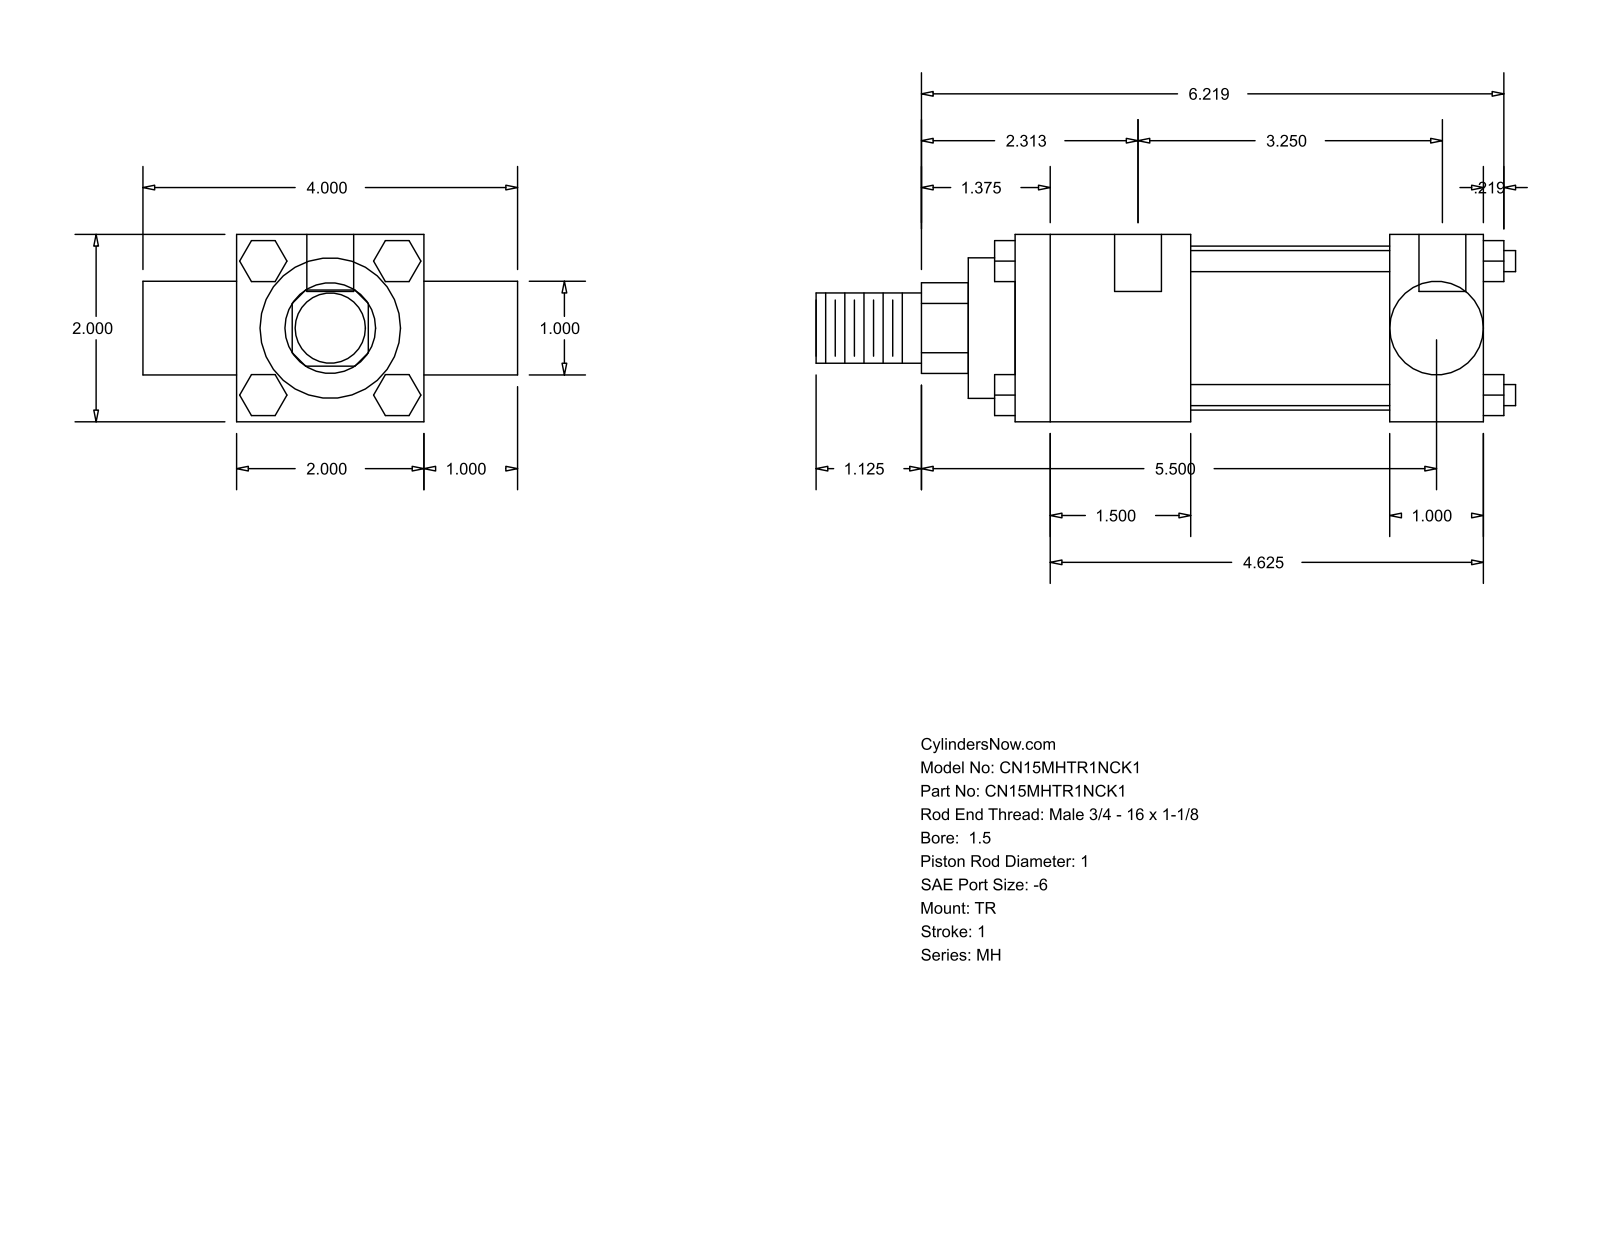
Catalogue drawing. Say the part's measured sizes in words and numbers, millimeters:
The part is named "MH_TR__0150_1". Its 3-D file was written by "GSSL Pune (CONFIG_CONTROL_DESIGN)". It is 0 solids with 120 faces: 92 planar, 28 cylindrical and 0 other. Overall it measures 189.71 by 101.6 by 50.8 millimeters. Round holes: 3 of diameter 5.56, 2 of diameter 12.7. Round bosses or shafts: 4 of diameter 5.71, 1 of diameter 44.45, 1 of diameter 38.1, 1 of diameter 25.4, 1 of diameter 25.35, 1 of diameter 19.05. Partial cylindrical surfaces (rounded edges, fillets, slot ends): 1 of radius 12.29. The main face-to-face distances are 50.8, 25.4, 101.6, 53.97, 127, 76.2, 47.63, 79.37, 12.7, 5.56. The hole center spacings are 3.18, 82.55, 85.73.
